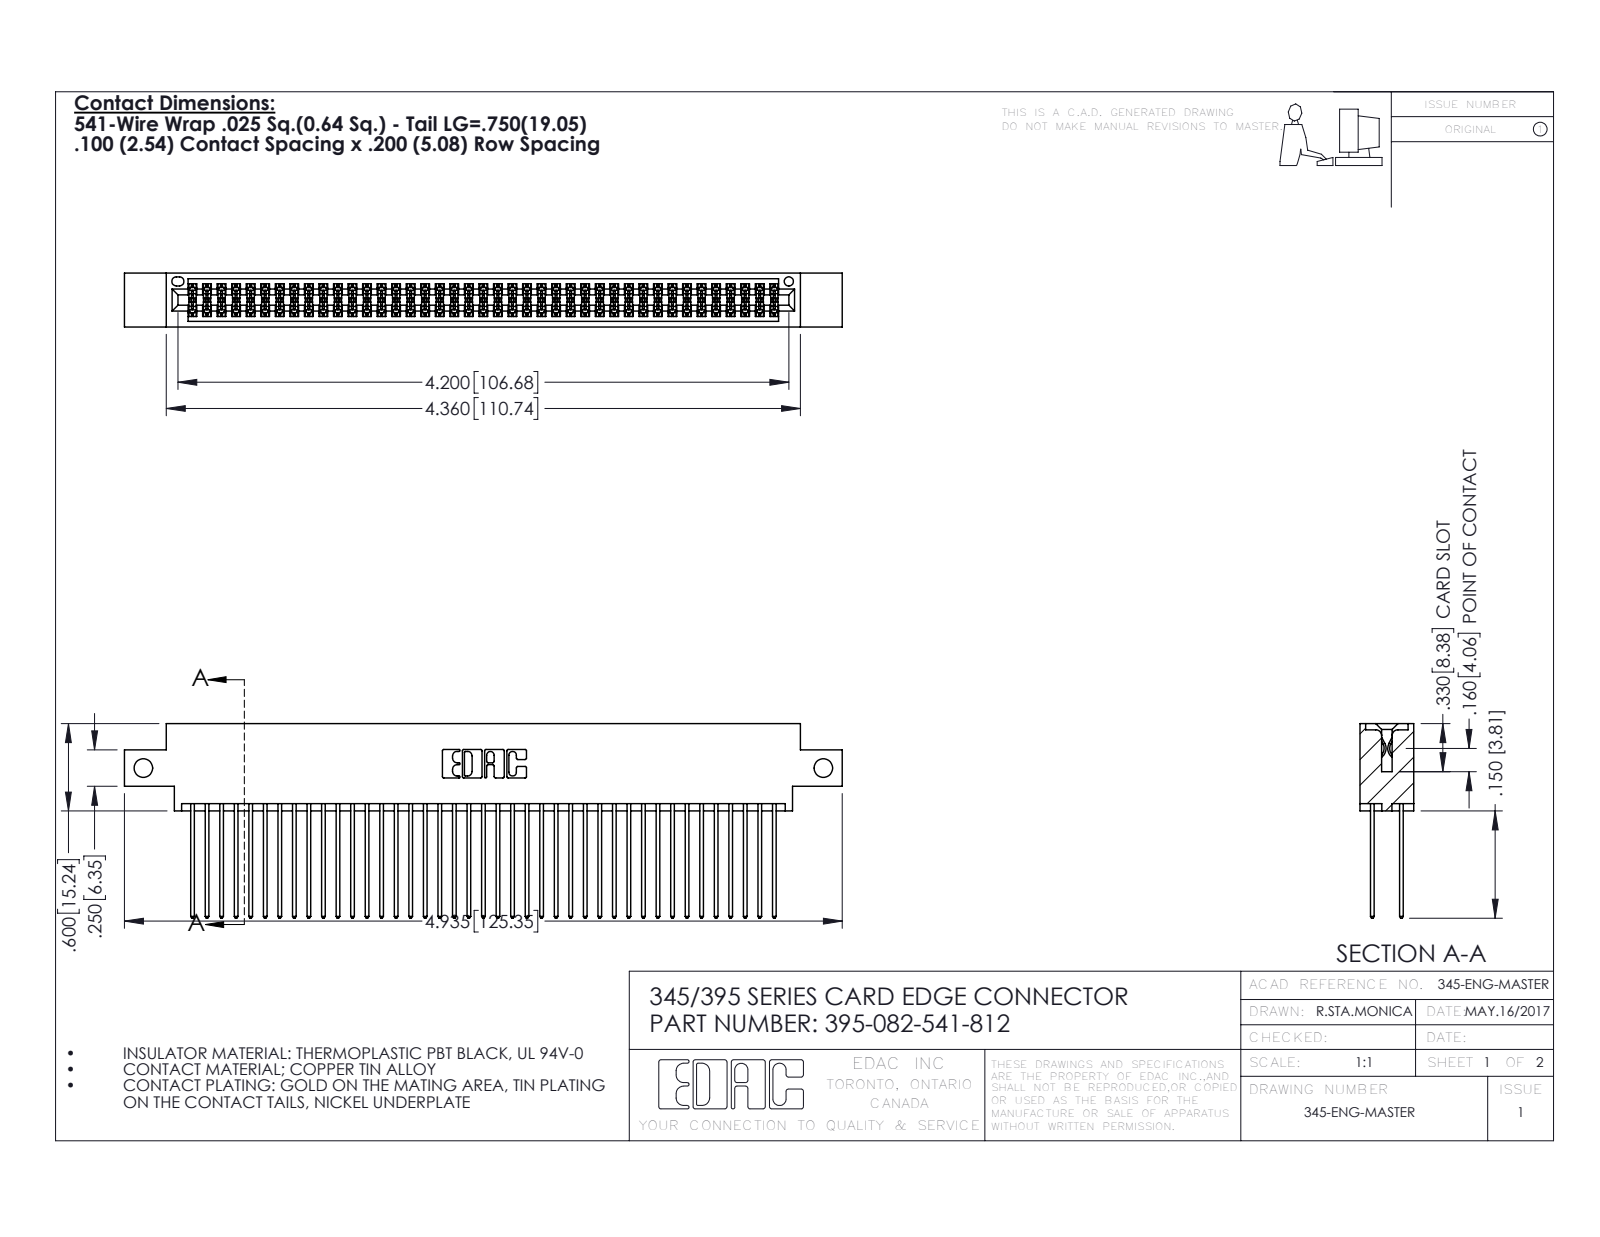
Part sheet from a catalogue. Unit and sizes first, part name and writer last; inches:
Units: inches
Overall size (bounding box): 4.935 × 1.337 × 0.37
Round holes (diameter × count): ⌀0.128 ×2, ⌀0.064 ×1
Partial cylindrical surfaces — rounded edges, fillets, slot ends (radius × count): R0.006 ×123, R0.01 ×82, R0.01 ×22, R0.007 ×6, R0.031 ×6, R0.026 ×3, R0.014 ×2, R0.019 ×2
Main face-to-face distances: 0.298, 0.072, 0.2, 0.098, 0.272, 0.025, 0.37, 0.225, 0.175, 0.149
Hole centre spacings: 4.675
Volume: 0.759 in³ · Surface area: 31.91 in²
Bodies: 83 solids, 4230 faces (2790 planar, 1440 cylindrical, 0 other)
Part name (STEP PRODUCT): 345-292-001_345-293-141; 345 Part_0.170 Offset - Side Mount; 395-082-541-812
STEP written by: SolidWorks 2016 (CONFIG_CONTROL_DESIGN)
